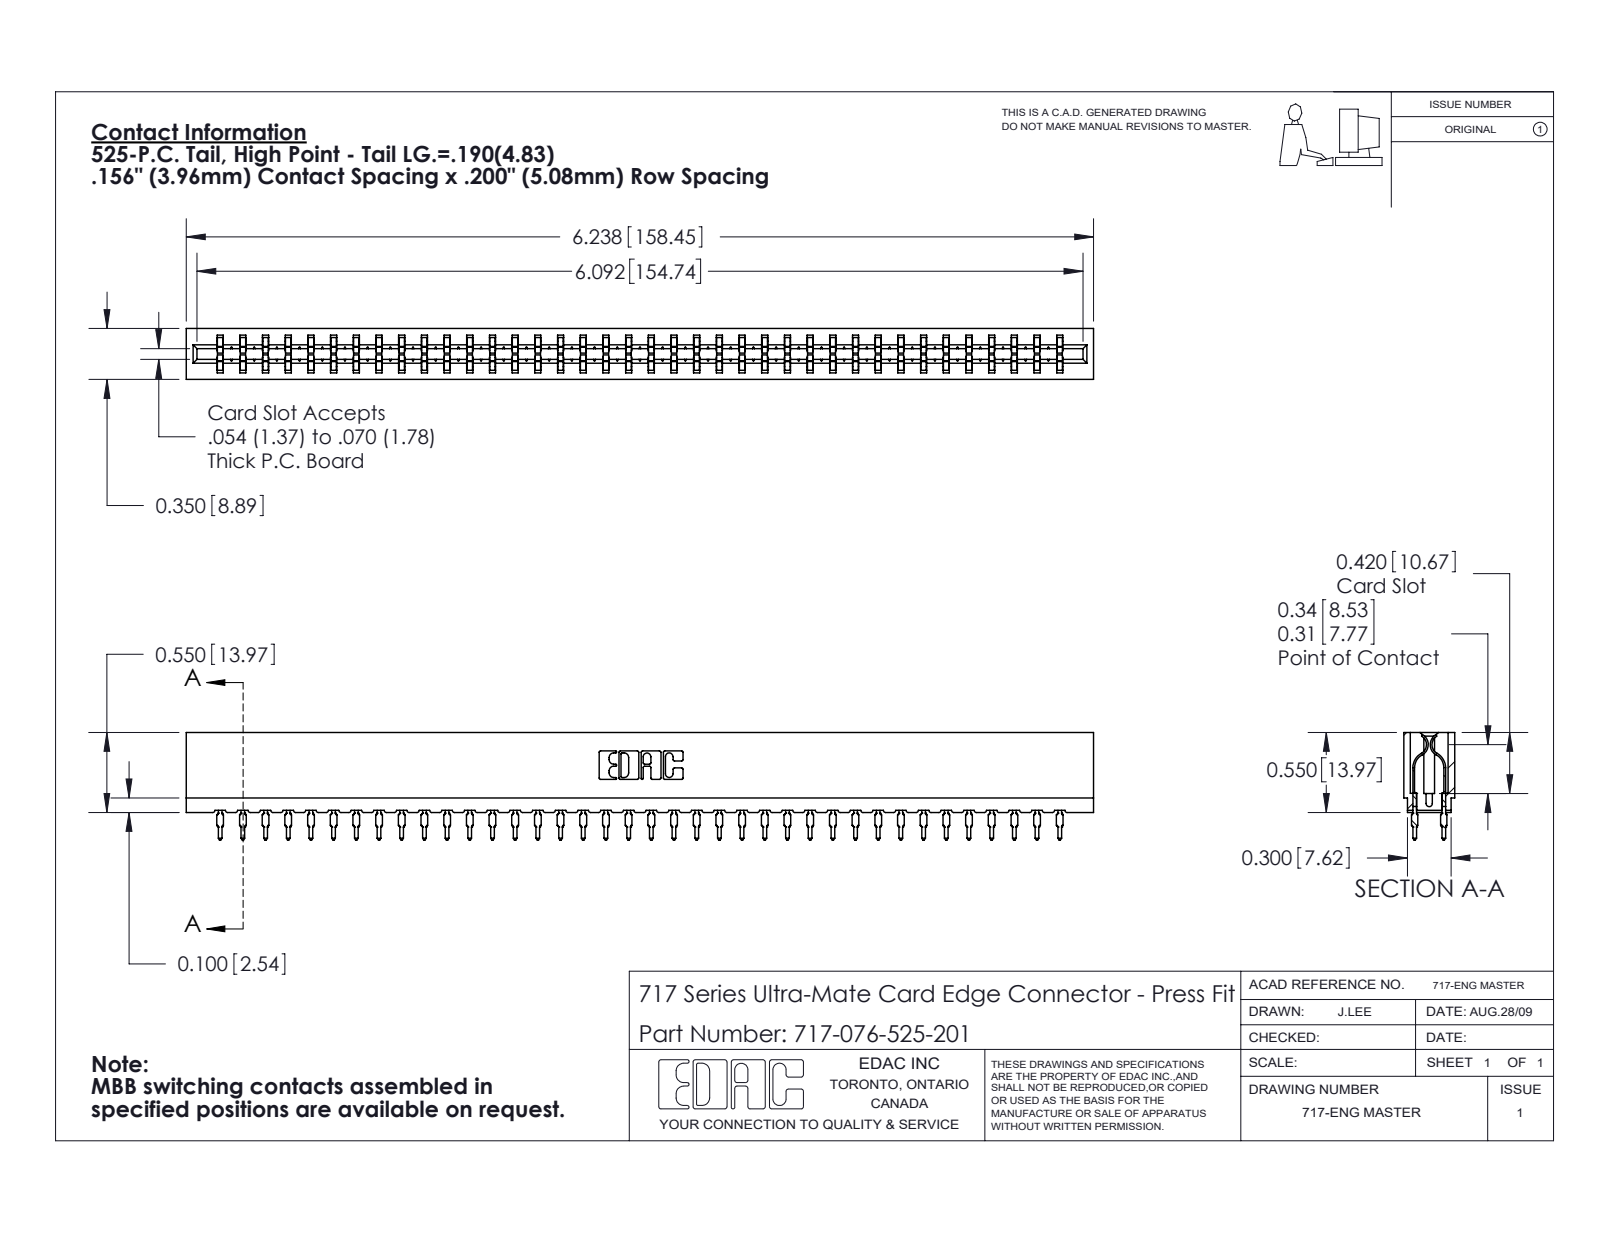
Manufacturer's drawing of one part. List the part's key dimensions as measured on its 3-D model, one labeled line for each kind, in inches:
Part name (STEP PRODUCT): 745-292-001_525; 717-076-525-201; 717 Part_Insulator Option - 06
STEP written by: SolidWorks 2020 (CONFIG_CONTROL_DESIGN)
Units: inches
Bodies: 77 solids, 6934 faces (3588 planar, 1370 cylindrical, 1976 other)
Overall size (bounding box): 6.238 × 0.739 × 0.35
Volume: 0.838 in³ · Surface area: 32.33 in²
Partial cylindrical surfaces — rounded edges, fillets, slot ends (radius × count): R0.021 ×152, R0.015 ×76, R0.01 ×22, R0.005 ×8, R0.011 ×8, R0.007 ×6, R0.031 ×6, R0.026 ×3
Main face-to-face distances: 0.212, 0.138, 0.35, 0.063, 0.287, 0.076, 0.149, 0.074, 0.045, 0.305
